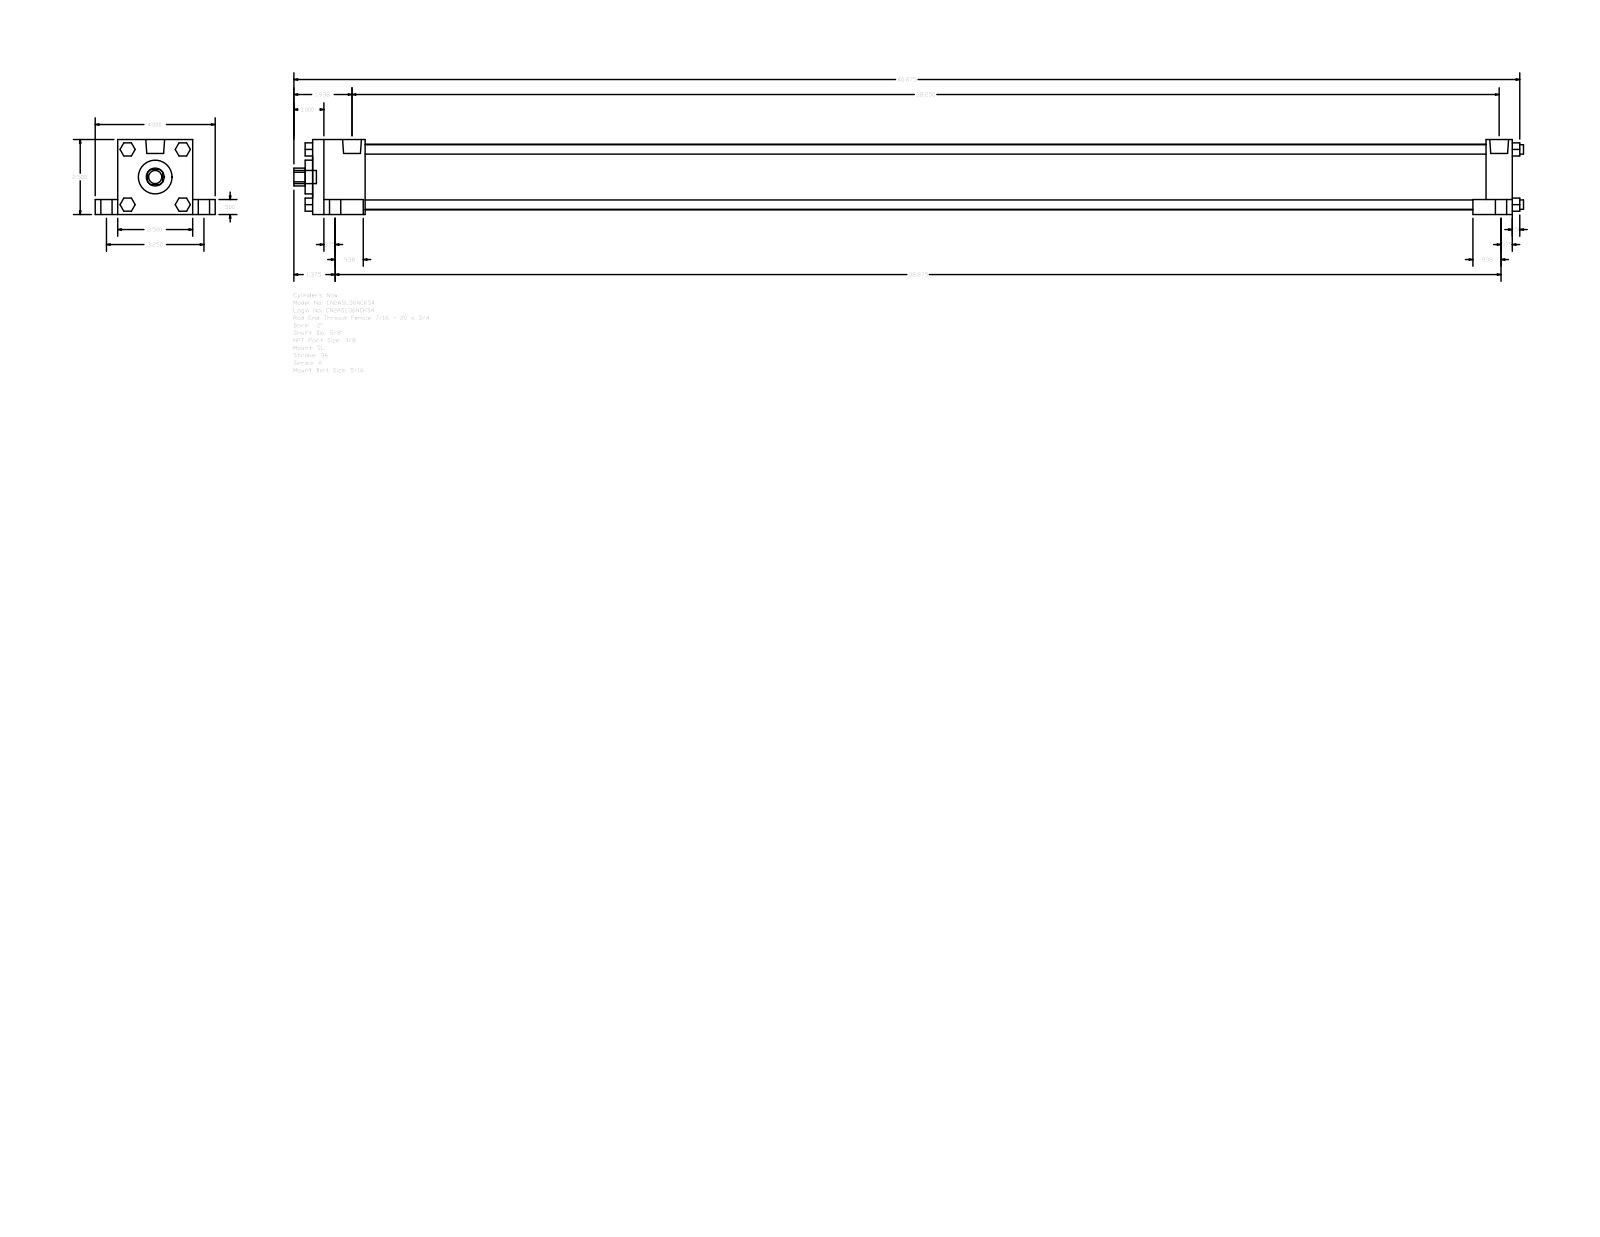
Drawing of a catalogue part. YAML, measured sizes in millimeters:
part_name: "A_SL__0200_0.625"
step_written_by: "GSSL Pune (CONFIG_CONTROL_DESIGN)"
units: millimeters
bodies: {solids: 0, faces: 148, planar: 112, cylindrical: 36, other: 0}
overall_size: [1041.4, 101.6, 63.5]
round_holes:
  - {diameter: 15.88, count: 1}
  - {diameter: 28.57, count: 1}
  - {diameter: 55.63, count: 1}
round_bosses_or_shafts:
  - {diameter: 15.88, count: 4}
  - {diameter: 9.53, count: 4}
  - {diameter: 7.94, count: 4}
  - {diameter: 5.56, count: 4}
  - {diameter: 15.93, count: 2}
  - {diameter: 11.11, count: 1}
partial_cylinders:
  - {radius: 7.54, count: 1}
face_to_face_distances: [63.5, 1016, 50.8, 12.7, 19.05, 82.55, 44.45, 971.55, 993.77, 949.32]
